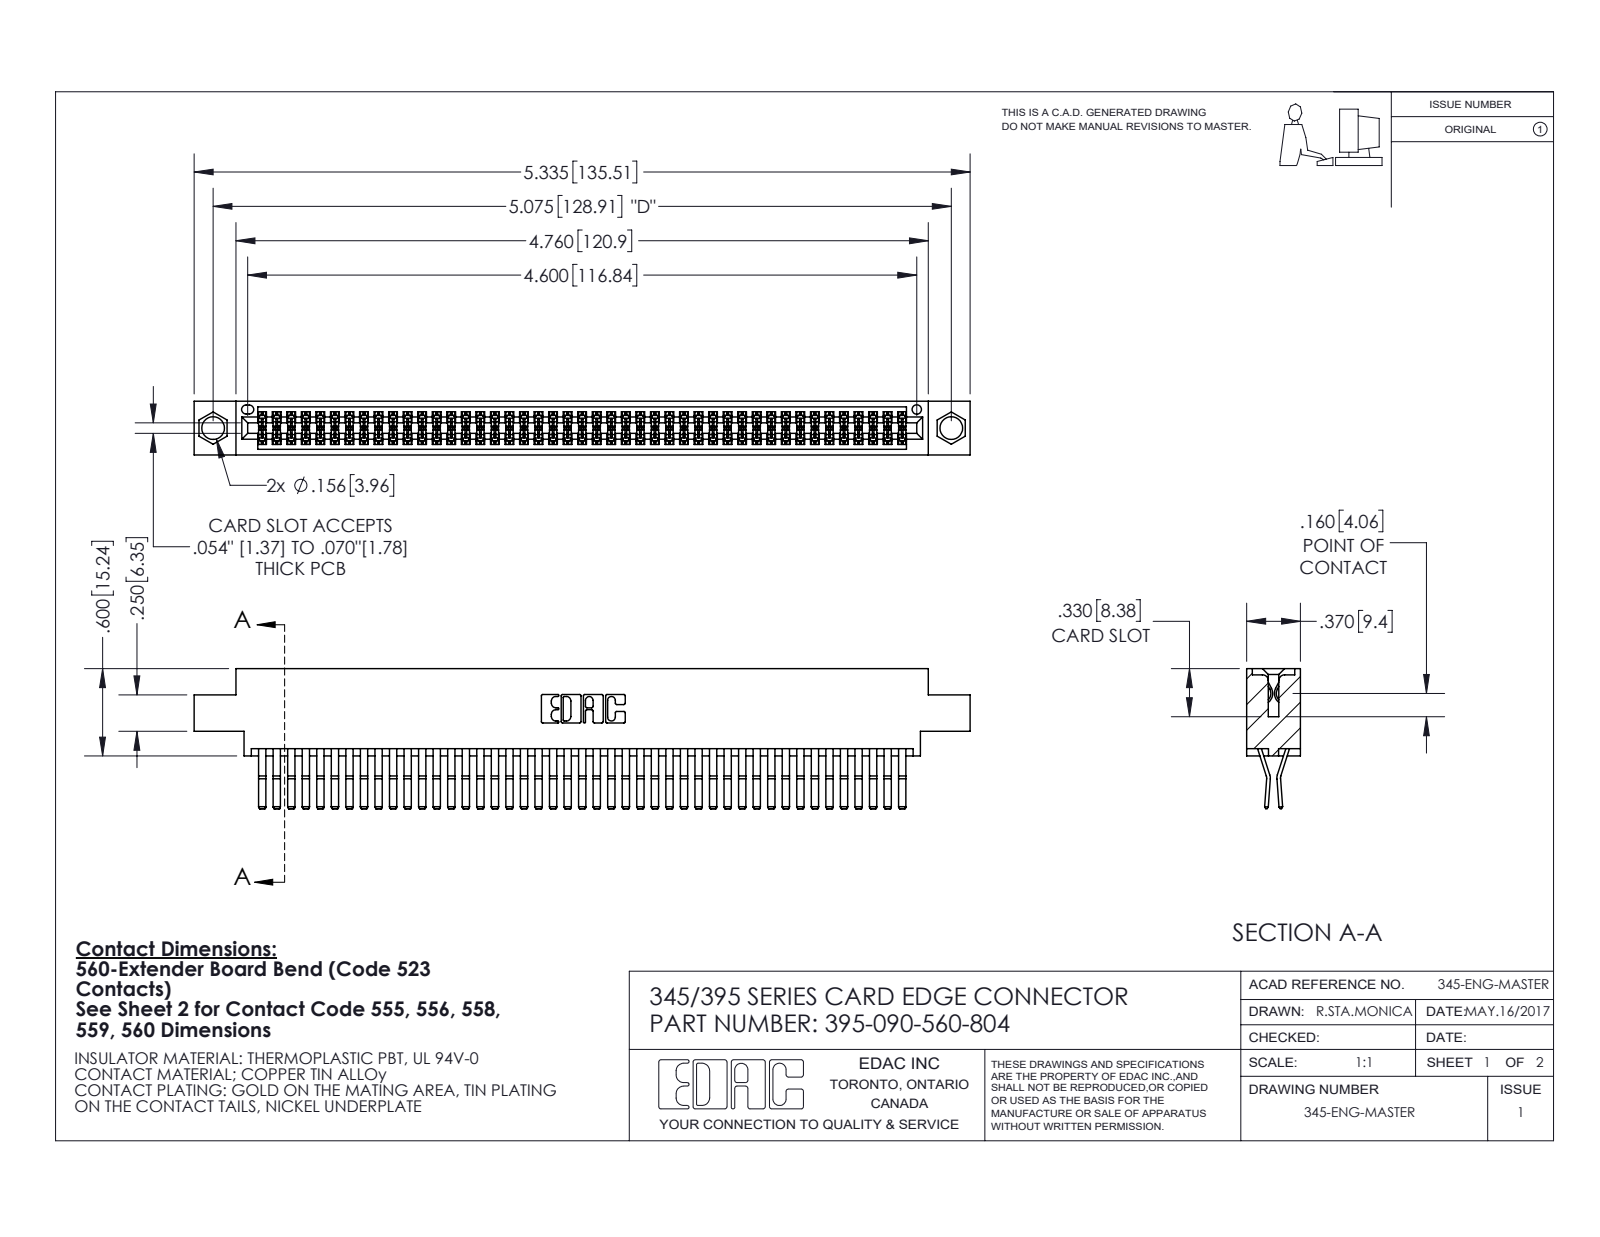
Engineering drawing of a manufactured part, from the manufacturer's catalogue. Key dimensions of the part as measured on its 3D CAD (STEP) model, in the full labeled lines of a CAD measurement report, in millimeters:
Part name (STEP PRODUCT): 395-090-560-804; 345 Part_0.170 Offset - 0.156 Dia-TI; 345-292-001_560 Tail
STEP written by: SolidWorks 2020 (CONFIG_CONTROL_DESIGN)
Units: millimetres
Bodies: 91 solids, 4824 faces (3068 planar, 1756 cylindrical, 0 other)
Overall size (bounding box): 135.5 × 24.4 × 9.4
Volume: 13 600 mm³ · Surface area: 21 620 mm²
Round holes (diameter × count): ⌀4 ×2, ⌀1.6 ×1
Partial cylindrical surfaces — rounded edges, fillets, slot ends (radius × count): R0.2 ×135, R0.3 ×22, R0.2 ×6, R0.8 ×6, R0.7 ×3, R0.3 ×2, R0.4 ×2, R0.5 ×2
Main face-to-face distances: 0.6, 7.6, 1.8, 9.4, 5.1, 2.5, 6.9, 5.7, 4.4, 3.8
Hole centre spacings: 6.9, 122.9, 128.9
